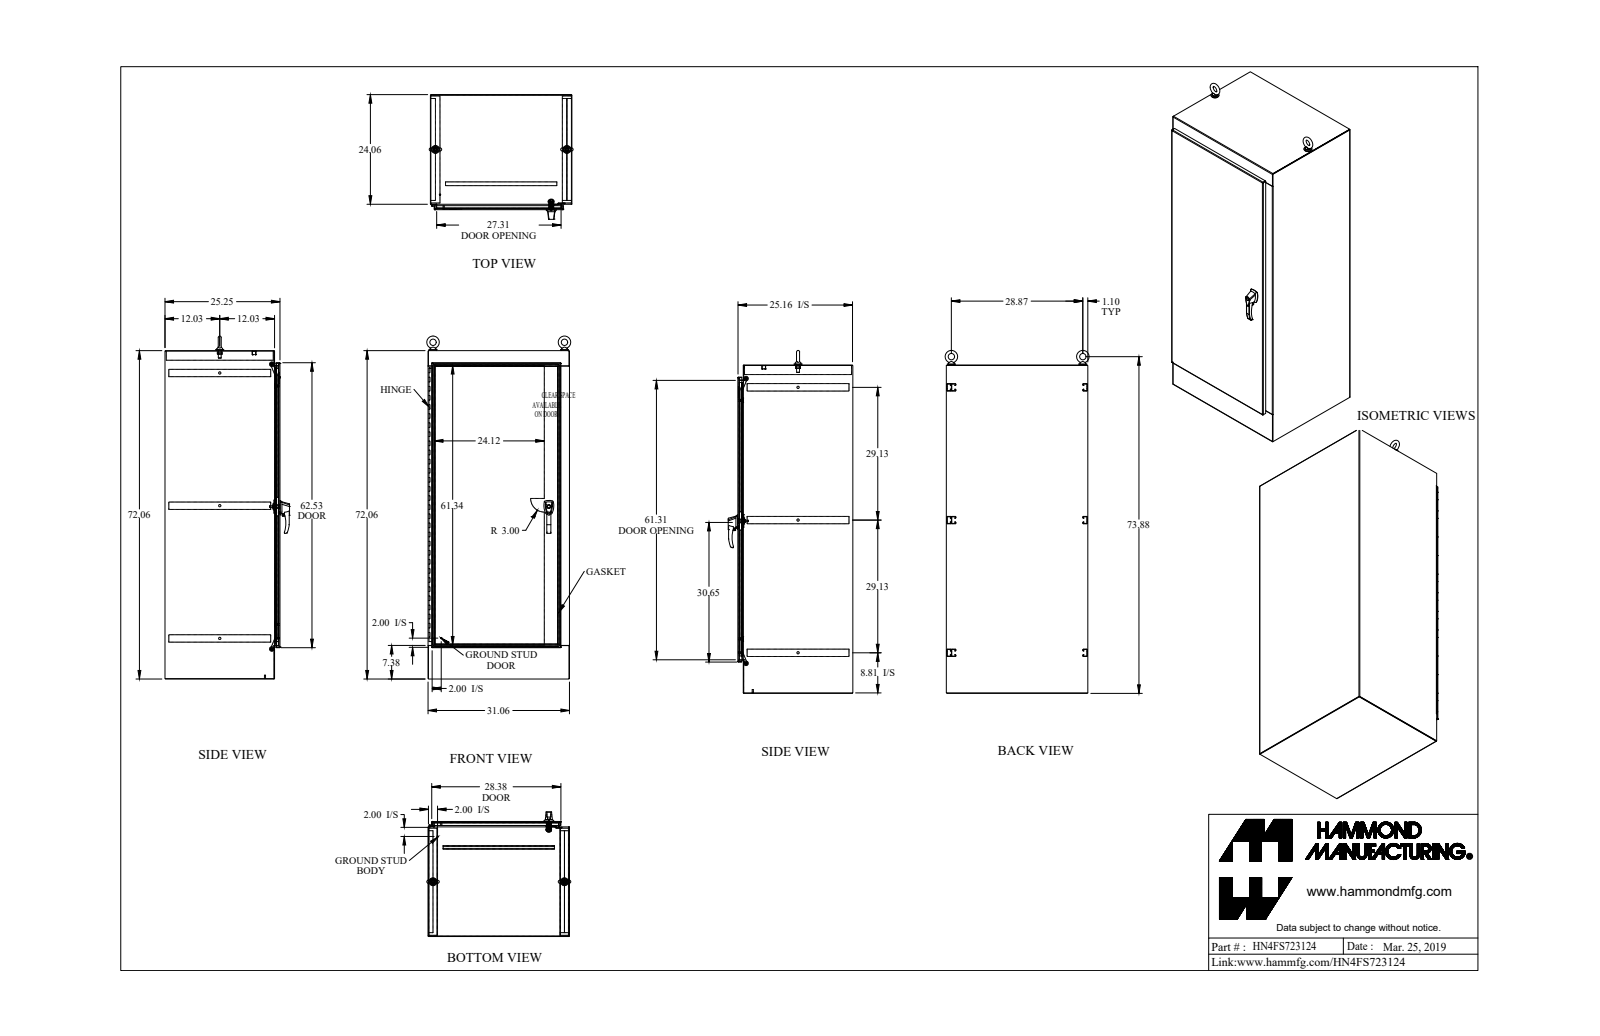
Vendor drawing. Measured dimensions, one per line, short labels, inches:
name: HN4FS723124
written by: SolidWorks 2018 (AUTOMOTIVE_DESIGN)
unit: in
bodies: 56 solids, 1977 faces (914 planar, 885 cylindrical, 178 other)
size: 75.25 × 31.604 × 27.362
volume: 1 111 in³; area: 23 338 in²
holes: 10× ⌀0.304, 7× ⌀0.35, 3× ⌀0.25, 3× ⌀0.5, 2× ⌀0.257, 2× ⌀0.28, 2× ⌀0.281, 2× ⌀0.313, 2× ⌀0.39, 2× ⌀0.413, 2× ⌀0.527, 2× ⌀0.687
bosses: 4× ⌀0.281, 2× ⌀1.75, 2× ⌀1.5, 2× ⌀1.25, 2× ⌀1, 2× ⌀0.75, 2× ⌀0.738, 2× ⌀0.63
rounds: 60× R0.043, 54× R0.138, 23× R0.5, 22× R0.125, 16× R0.017, 15× R0.048, 15× R0.06, 15× R0.143
face distances: 0.095, 0.095, 25.152, 30.965, 25.057, 30.87, 25.247, 31.06, 71.965, 23.965
hole spacings: 6, 12, 18, 24, 30, 36, 42, 0.015
